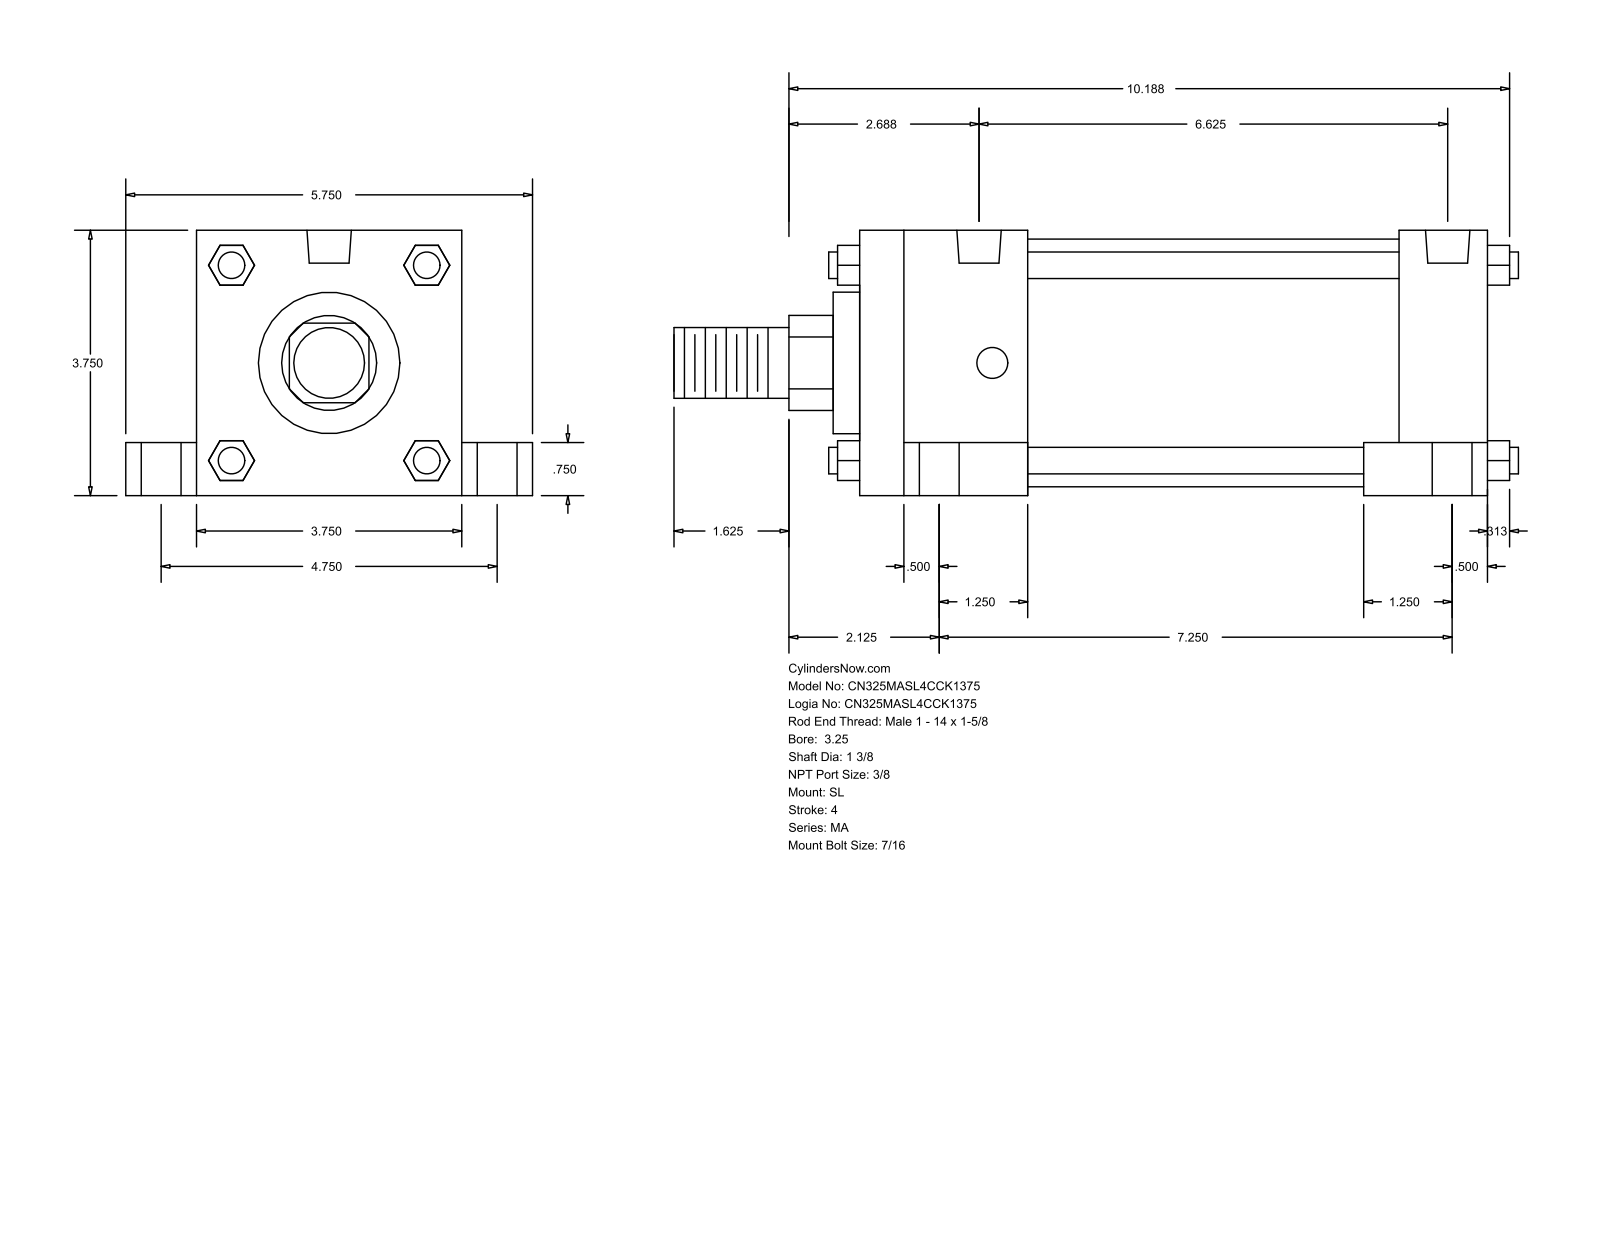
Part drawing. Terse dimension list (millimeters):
name: MA_SL__0325_1.375
written by: GSSL Pune (CONFIG_CONTROL_DESIGN)
unit: mm
bodies: 0 solids, 148 faces (112 planar, 36 cylindrical, 0 other)
size: 303.21 × 146.05 × 95.25
holes: 4× ⌀11.11, 4× ⌀14.29, 4× ⌀20.64, 2× ⌀15.93
bosses: 4× ⌀9.53, 1× ⌀88.9, 1× ⌀50.8, 1× ⌀34.92, 1× ⌀25.4
rounds: 1× R17.06
face distances: 95.24, 225.42, 133.35, 25.41, 120.65, 193.67, 31.75, 60.32, 165.1, 19.05
hole spacings: 60.35, 60.66, 62, 63.27, 120.66, 158.75, 175.77, 180.26
